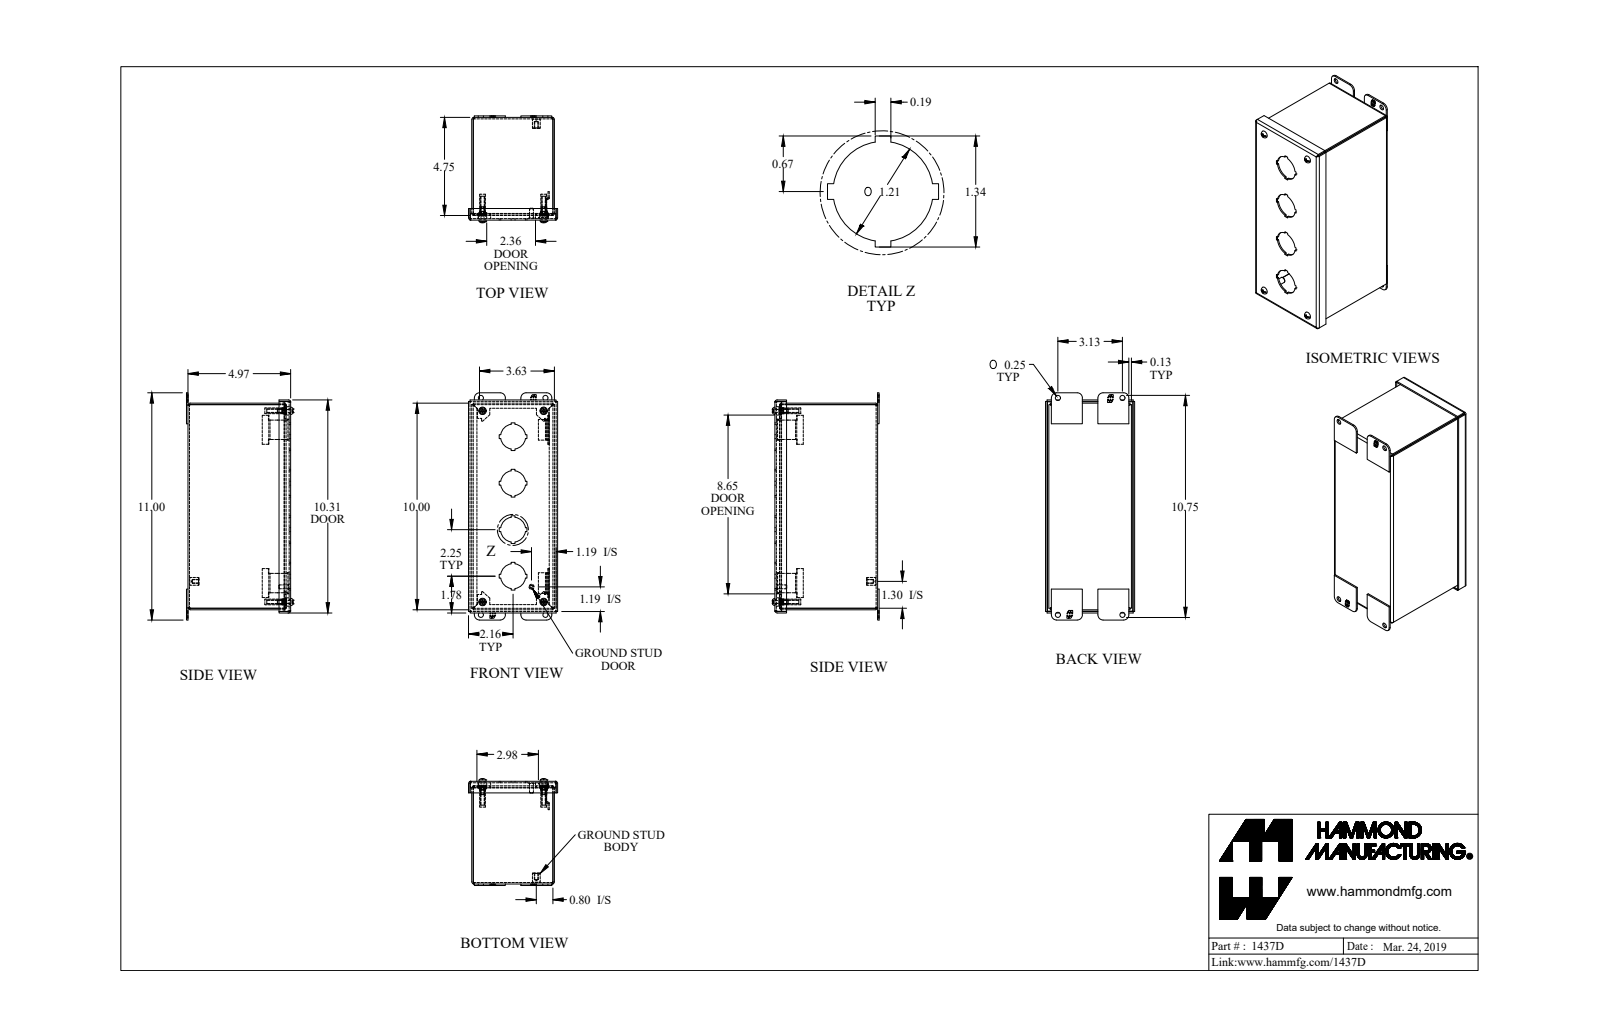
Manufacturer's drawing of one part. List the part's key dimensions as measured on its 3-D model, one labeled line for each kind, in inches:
Part name (STEP PRODUCT): 1437D_Default
STEP written by: SolidWorks 2019 (CONFIG_CONTROL_DESIGN)
Units: inches
Bodies: 23 solids, 779 faces (547 planar, 176 cylindrical, 56 other)
Overall size (bounding box): 11 × 5.171 × 4.312
Volume: 20.02 in³ · Surface area: 533.8 in²
Round holes (diameter × count): ⌀0.25 ×8, ⌀0.159 ×4, ⌀0.406 ×4, ⌀1.21 ×4, ⌀0.156 ×1
Round bosses / shafts (diameter × count): ⌀0.39 ×4, ⌀0.275 ×4, ⌀0.19 ×4, ⌀0.148 ×4, ⌀0.375 ×1, ⌀0.25 ×1, ⌀0.188 ×1
Partial cylindrical surfaces — rounded edges, fillets, slot ends (radius × count): R0.036 ×12, R0.108 ×12, R0.25 ×8, R0.029 ×4, R0.086 ×4, R0.16 ×4, R0.171 ×4, R0.125 ×2
Main face-to-face distances: 0.072, 3.928, 4.9, 4.972, 4, 3.856, 4.828, 9.928, 0.156, 4.084
Hole centre spacings: 9.25, 9.875, 10.333, 3.106, 0.631, 1.937, 2.961, 3.107
